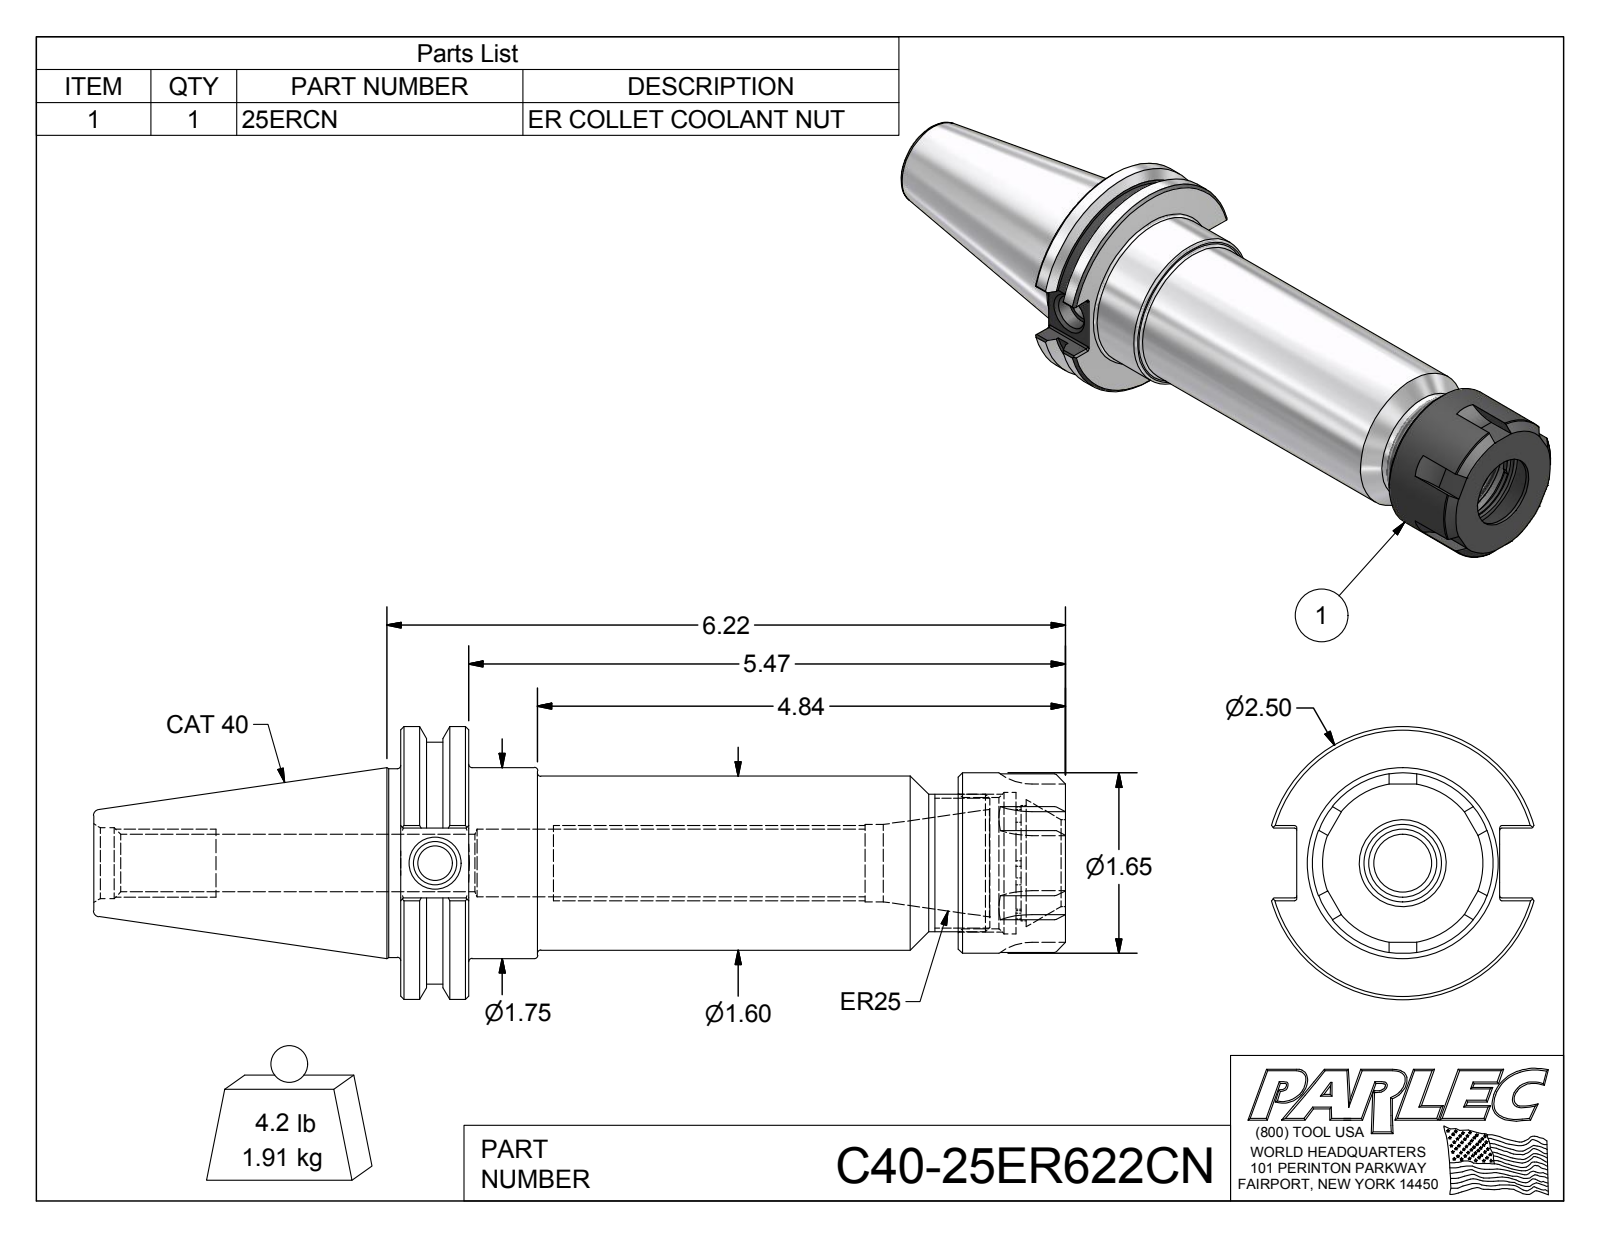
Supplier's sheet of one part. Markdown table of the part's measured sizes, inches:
| quantity | value |
| --- | --- |
| part name | C40-25ER622CN; C40-25ER6-1; 25ERCN |
| STEP written by | Autodesk Inventor 2012 (AUTOMOTIVE_DESIGN) |
| units | inches |
| bodies | 2 solids, 145 faces (61 planar, 44 cylindrical, 40 other) |
| overall size | 8.908 × 2.5 × 2.403 |
| volume | 14.77 in³ |
| surface area | 75.92 in² |
| round holes (diameter × count) | 0.315 × 1, 0.399 × 1, 0.527 × 1, 0.62 × 1, 0.648 × 1, 0.71 × 1, 0.794 × 1, 1.057 × 1, 1.201 × 1, 1.294 × 1 |
| round bosses / shafts (diameter × count) | 2.5 × 1, 2.219 × 1, 1.75 × 1, 1.73 × 1, 1.654 × 1, 1.595 × 1, 1.26 × 1 |
| partial cylindrical surfaces (radius × count) | 0.02 × 12, 0.5 × 6, 0.472 × 1, 0.515 × 1 |
| main face-to-face distances | 0.625, 6.095, 5.47, 5.111, 4.486, 0.984, 5.642, 5.017, 0.531, 0.453 |
